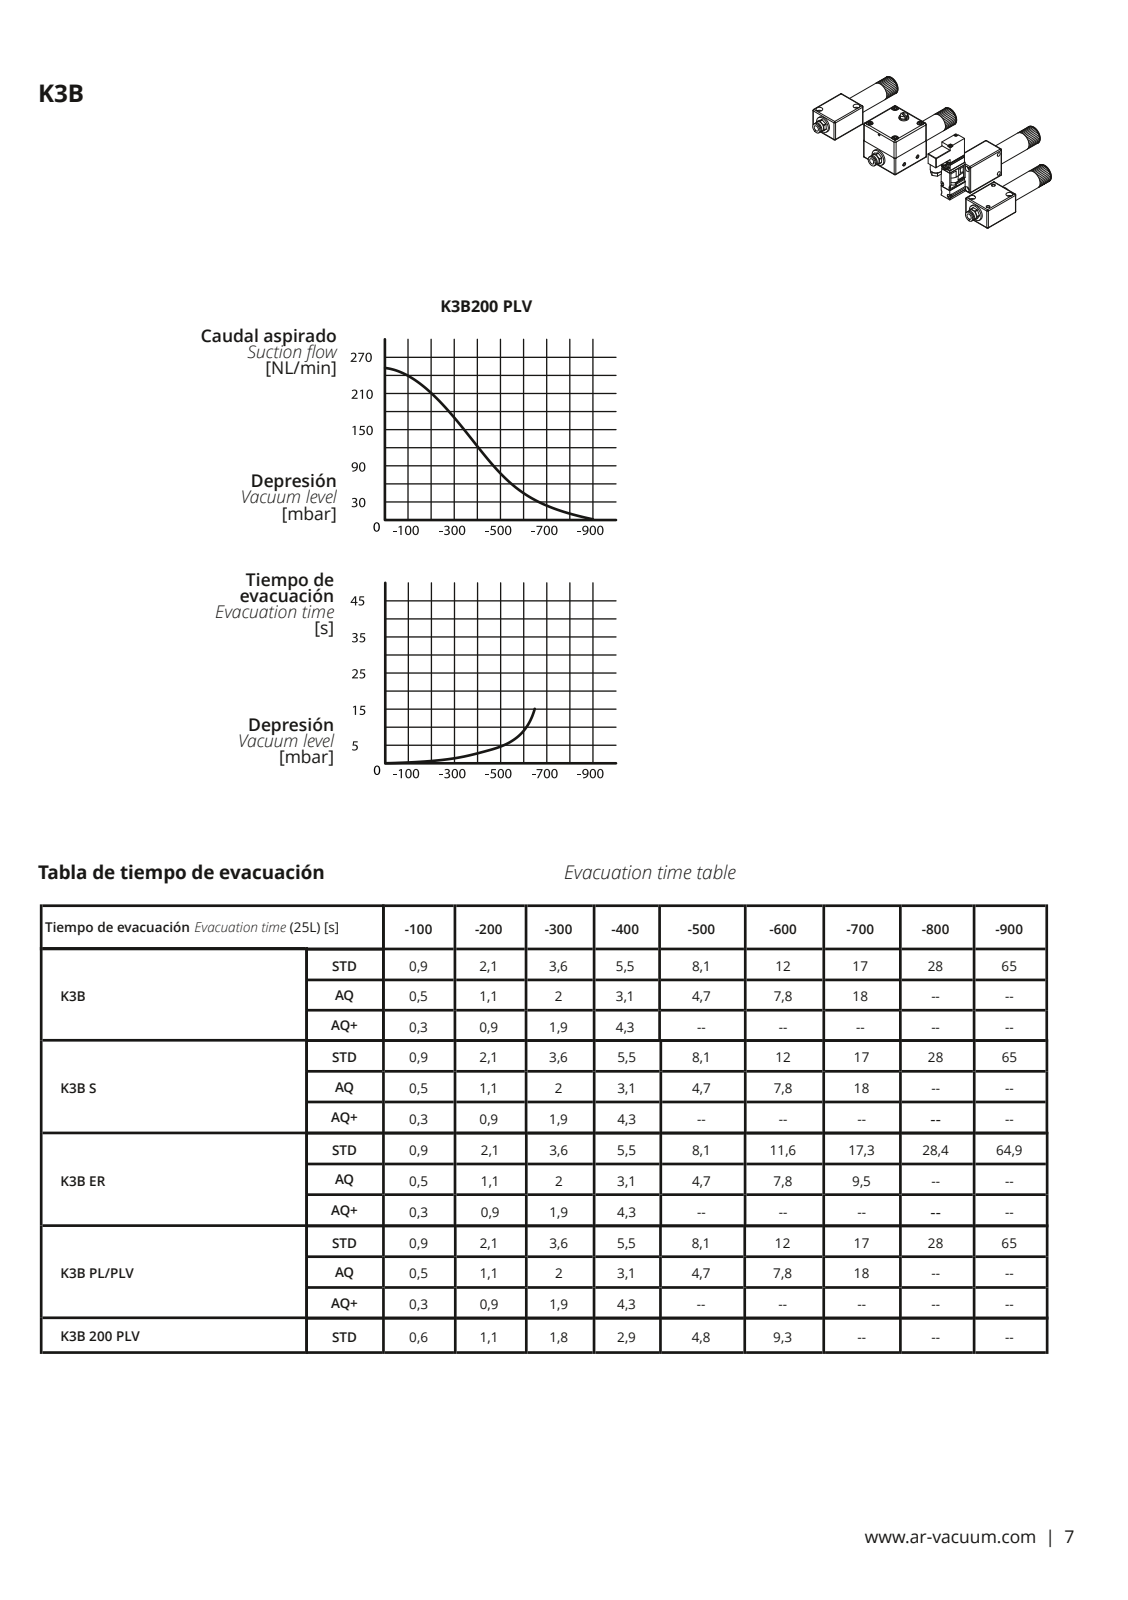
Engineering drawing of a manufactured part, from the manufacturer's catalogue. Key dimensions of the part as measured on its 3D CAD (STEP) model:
Part name (STEP PRODUCT): Pieza1
STEP written by: Autodesk Inventor 2019 (AUTOMOTIVE_DESIGN)
Units: millimetres
Bodies: 1 solid, 186 faces (134 planar, 37 cylindrical, 15 other)
Overall size (bounding box): 142.9 × 42 × 30
Volume: 92 321 mm³ · Surface area: 22 700 mm²
Round holes (diameter × count): ⌀4.13 ×2, ⌀5.25 ×2, ⌀9 ×2, ⌀18.63 ×2, ⌀5 ×1, ⌀8 ×1, ⌀10 ×1, ⌀16 ×1
Round bosses / shafts (diameter × count): ⌀25 ×1, ⌀22 ×1, ⌀21.6 ×1, ⌀13.6 ×1, ⌀9.2 ×1
Partial cylindrical surfaces — rounded edges, fillets, slot ends (radius × count): R1.5 ×12, R7.9 ×1
Main face-to-face distances: 30, 42, 54, 129.1, 75.1, 24.91, 20.5, 9.5, 43, 11
Hole centre spacings: 22.67, 27.46, 30, 40, 50
